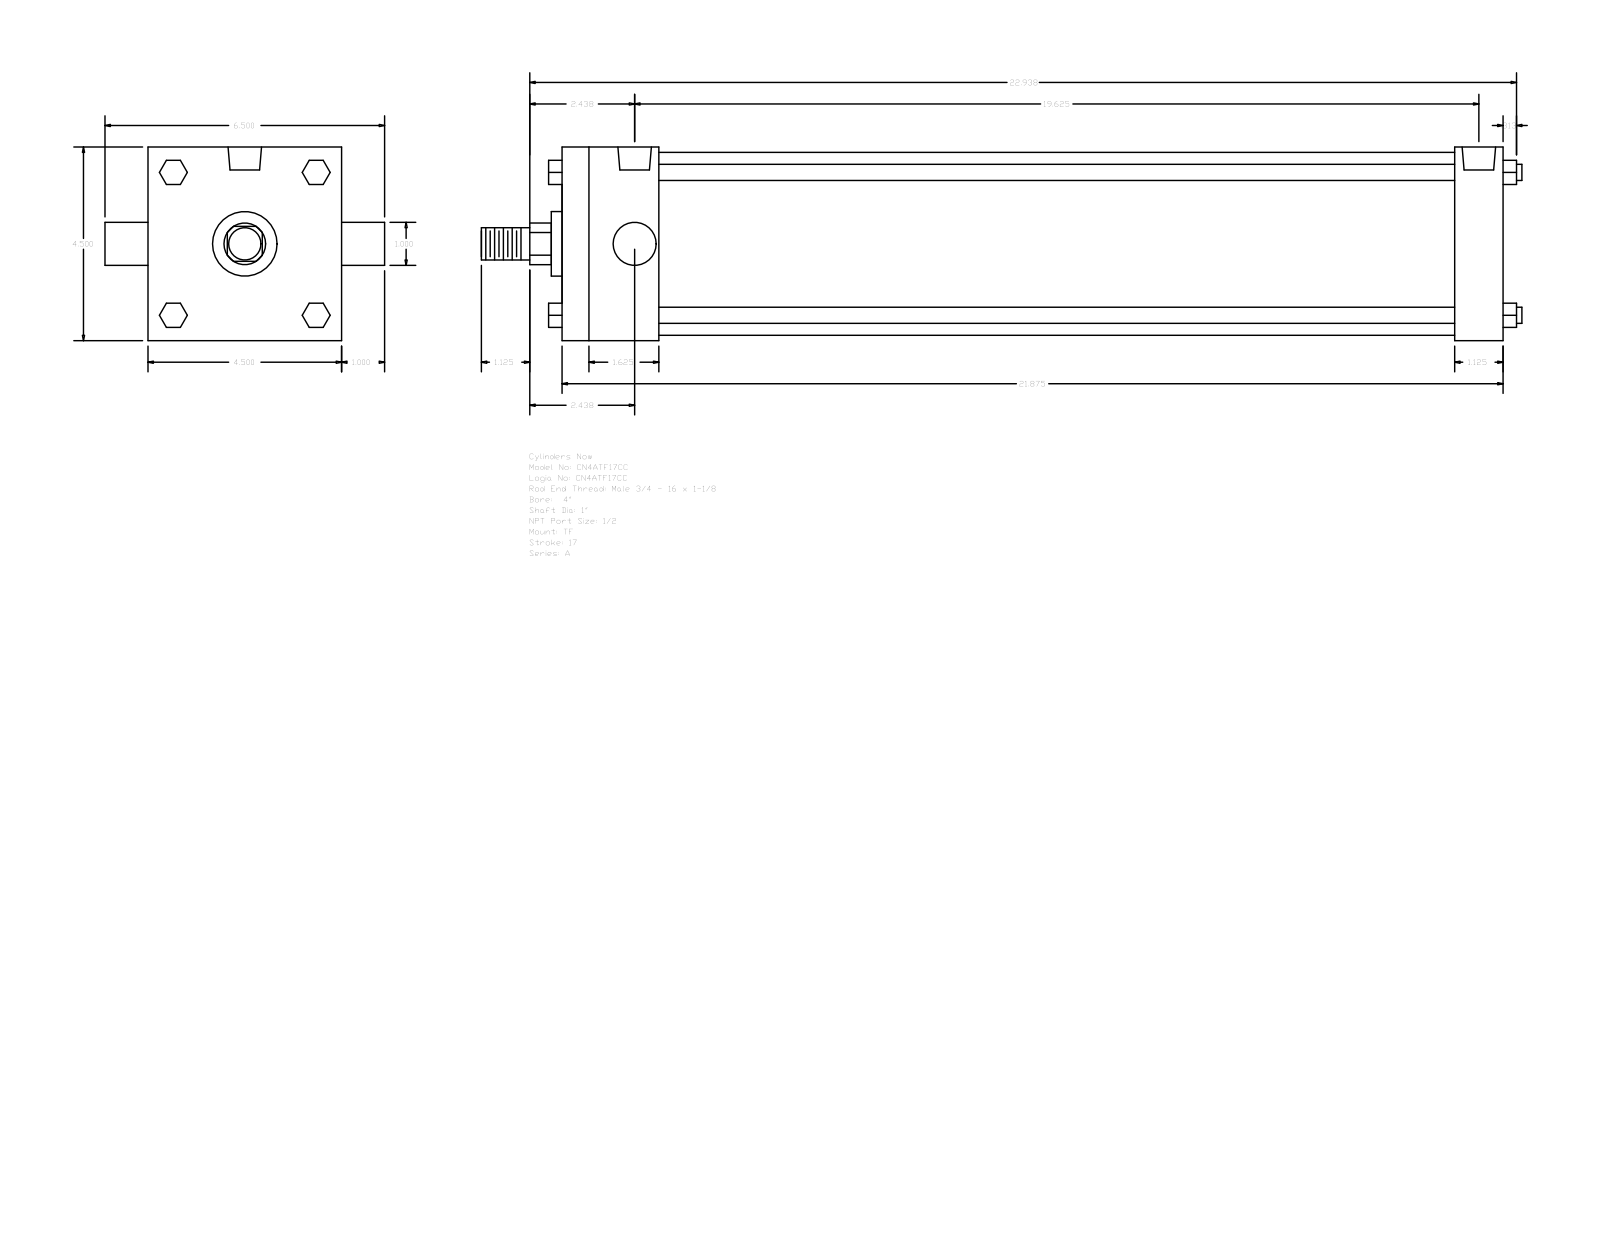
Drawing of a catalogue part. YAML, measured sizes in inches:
part_name: "A_TF__0400_1"
step_written_by: "GSSL Pune (CONFIG_CONTROL_DESIGN)"
units: inches
bodies: {solids: 0, faces: 120, planar: 92, cylindrical: 28, other: 0}
overall_size: [24.187, 6.5, 4.5]
round_holes:
  - {diameter: 0.344, count: 3}
  - {diameter: 0.778, count: 2}
round_bosses_or_shafts:
  - {diameter: 0.375, count: 4}
  - {diameter: 1, count: 2}
  - {diameter: 4.25, count: 1}
  - {diameter: 1.5, count: 1}
  - {diameter: 0.75, count: 1}
partial_cylinders:
  - {radius: 0.484, count: 1}
face_to_face_distances: [4.5, 21.875, 1.125, 20.75, 2.25, 18.5, 19.625, 0.563, 1.66, 2.875]
hole_center_spacings: [0.125, 19.5, 19.375, 19.625]
